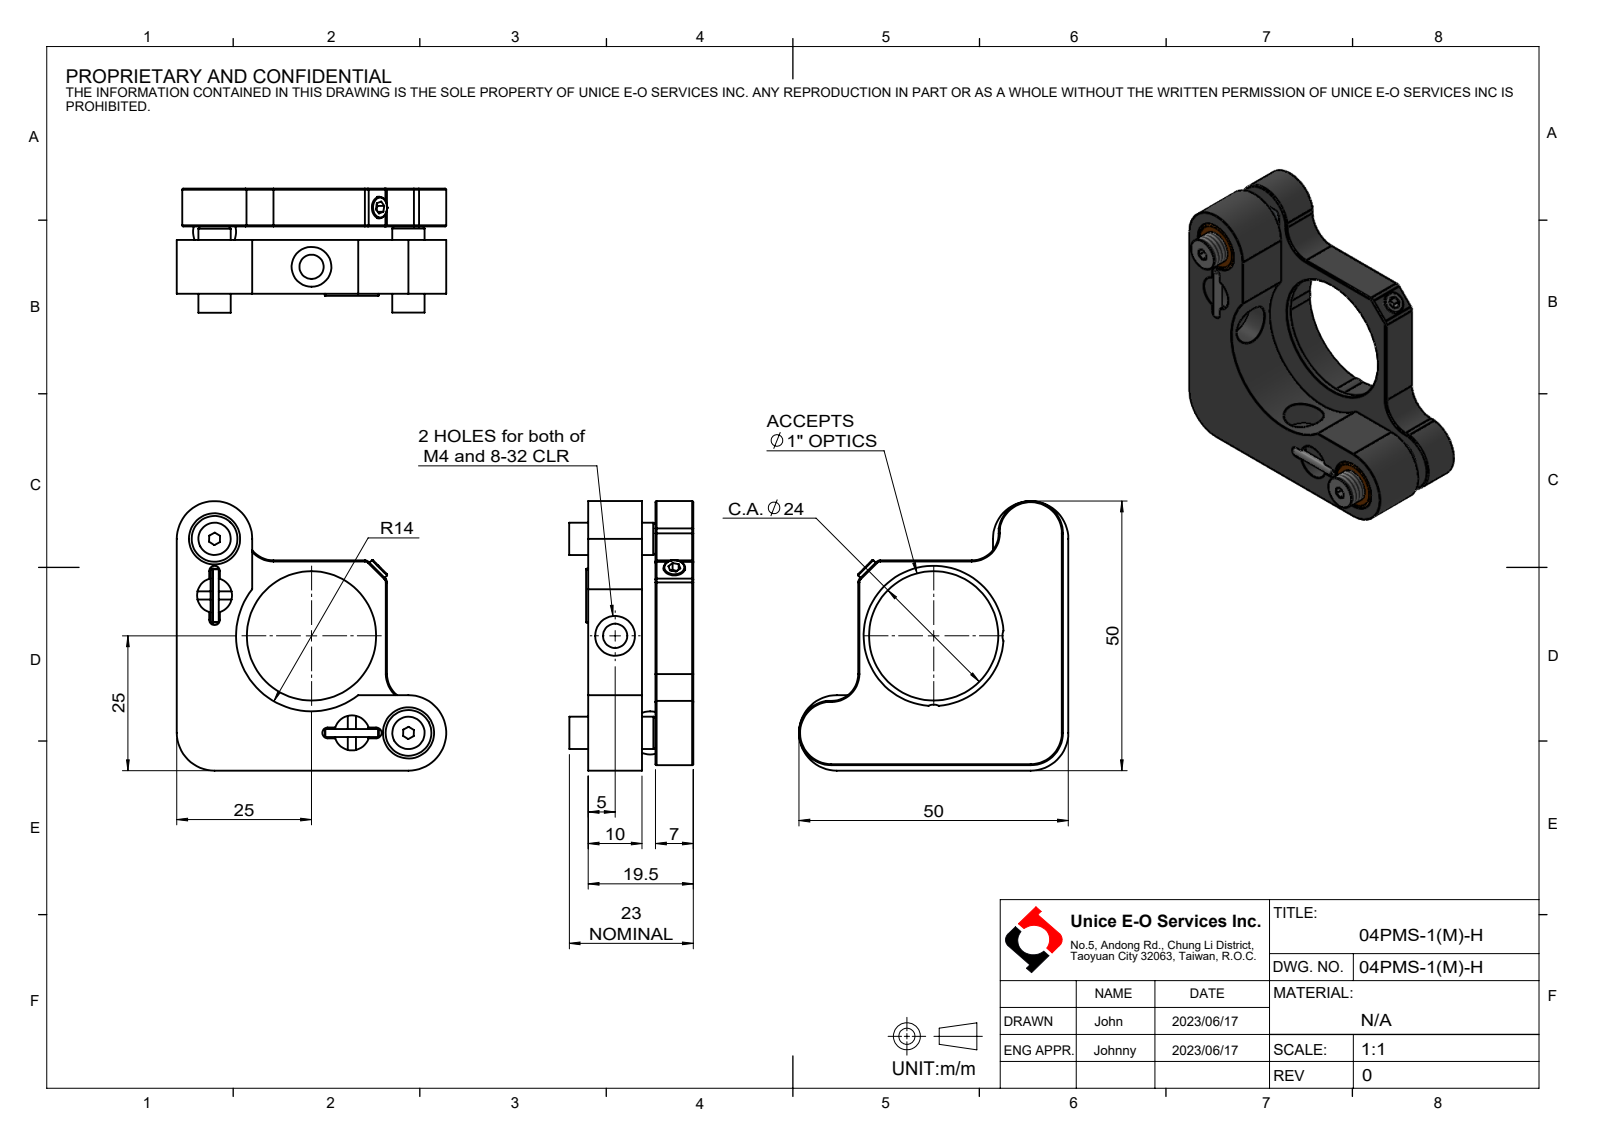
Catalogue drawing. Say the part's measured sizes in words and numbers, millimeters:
The part is named "04PMS-1(M)-H". Its 3-D file was written by "SolidWorks 2022 (CONFIG_CONTROL_DESIGN)". It is 0 solids with 163 faces: 68 planar, 62 cylindrical and 33 other. Overall it measures 50 by 50 by 23.04 millimeters. Round holes: 4 of diameter 1, 2 of diameter 1.7, 2 of diameter 4.5, 2 of diameter 6.5, 2 of diameter 7.4, 2 of diameter 9.5, 1 of diameter 3.3, 1 of diameter 24, 1 of diameter 26. Round bosses or shafts: 6 of diameter 1.5, 2 of diameter 6, 1 of diameter 4, 1 of diameter 1.6. Partial cylindrical surfaces (rounded edges, fillets, slot ends): 14 of radius 0.2, 6 of radius 1, 3 of radius 6, 3 of radius 7, 2 of radius 2.5, 2 of radius 5, 1 of radius 1.5, 1 of radius 14. The main face-to-face distances are 7, 19.5, 12.5, 10, 9.5, 2.5, 1, 39, 38, 14. The hole center spacings are 10.5, 13.73, 19.5, 25.46, 44.12, 18.56, 18.62, 30.16.
